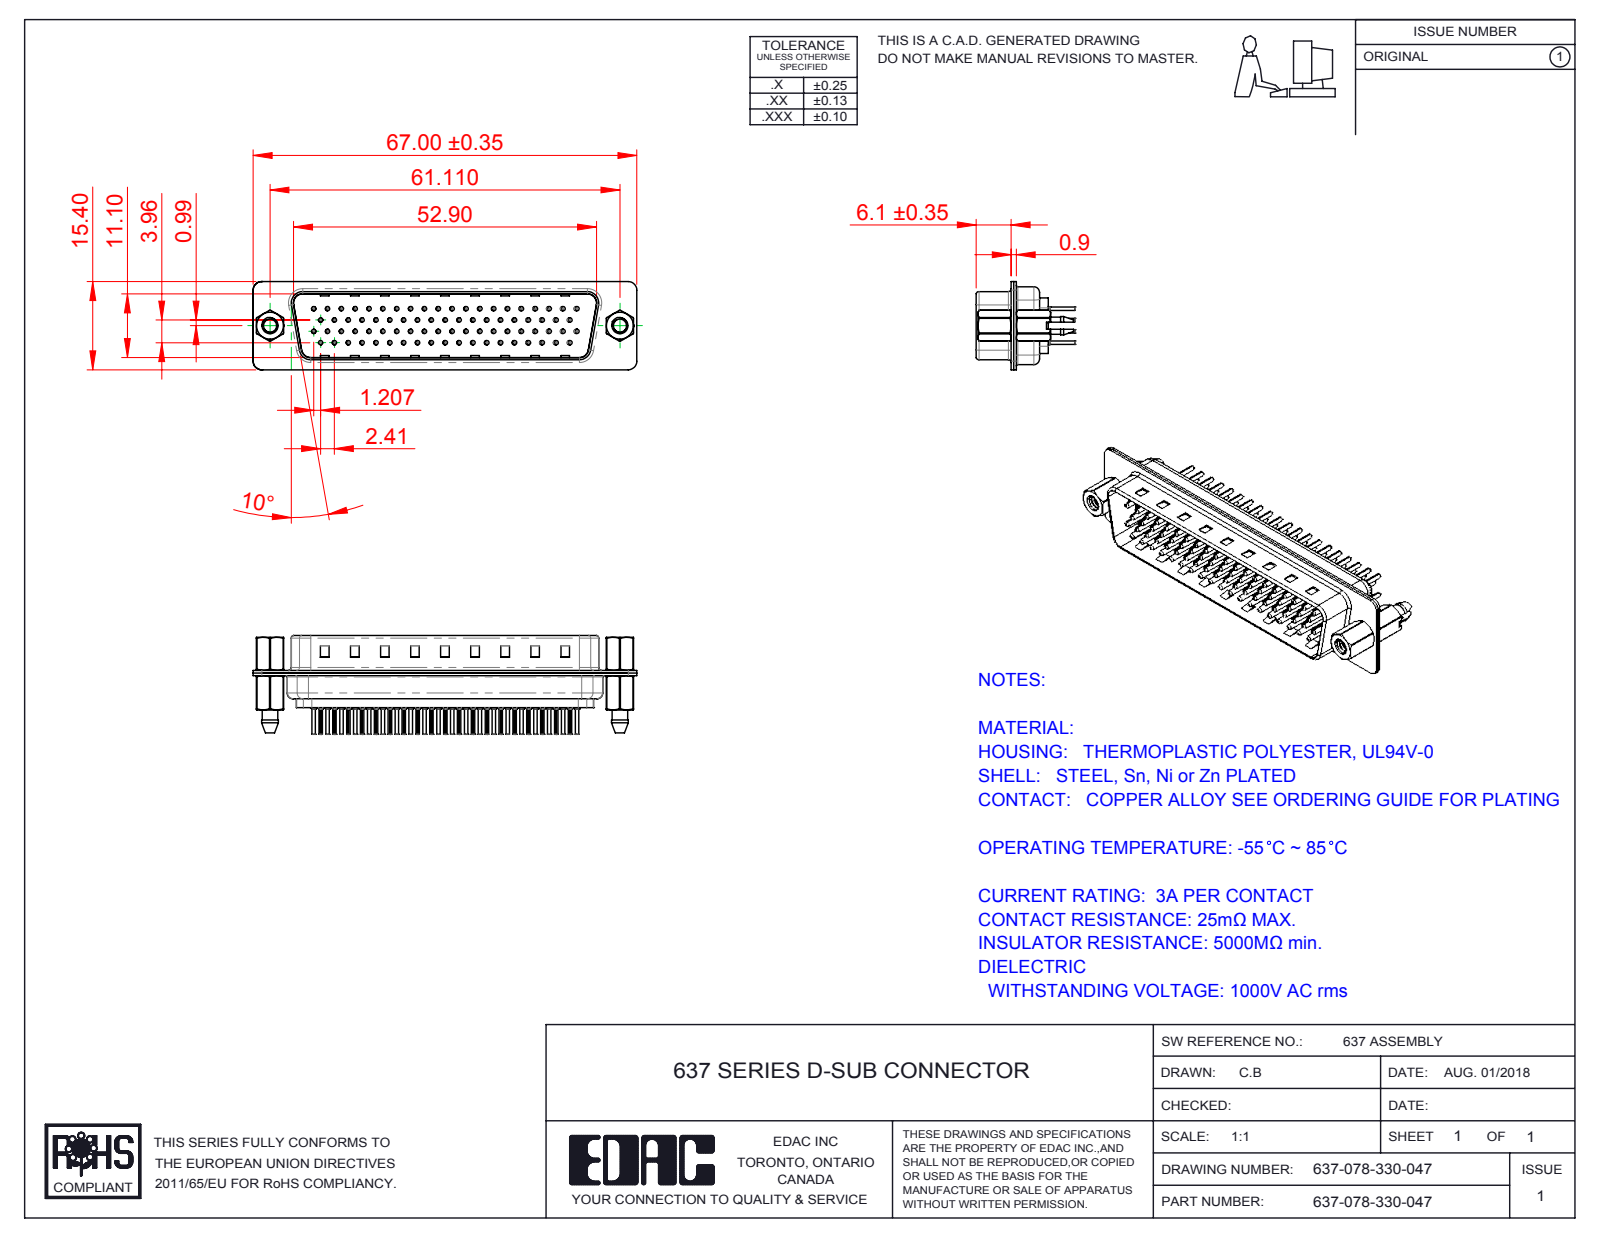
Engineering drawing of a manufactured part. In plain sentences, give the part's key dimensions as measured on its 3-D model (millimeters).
The part is named "637 Contact Row 3_30; 637 Shell Rear_78 Contacts; 637 Contact Row 78_30; 637 Contact Row 1_30 (+6 more)". Its 3-D file was written by "SolidWorks 2016 (CONFIG_CONTROL_DESIGN)". It is 85 solids with 8412 faces: 2129 planar, 3131 cylindrical and 3152 other. Overall it measures 67 by 17.25 by 15.4 millimeters. Its volume is 4 660 cubic millimeters and its surface area 16 633 square millimeters. Round holes: 150 of diameter 1.6, 78 of diameter 0.2, 78 of diameter 0.35, 78 of diameter 1.1, 72 of diameter 0.75, 72 of diameter 2, 3 of diameter 4, 2 of diameter 2.26, 2 of diameter 2.29, 2 of diameter 4.8. Round bosses or shafts: 78 of diameter 2, 78 of diameter 1.5, 78 of diameter 0.75, 78 of diameter 0.6, 2 of diameter 4.9, 2 of diameter 2.79, 1 of diameter 4.8. Partial cylindrical surfaces (rounded edges, fillets, slot ends): 156 of radius 0.1, 18 of radius 1.5, 12 of radius 2, 8 of radius 0.5, 6 of radius 1.6, 4 of radius 0.25, 4 of radius 0.55, 4 of radius 0.7. The main face-to-face distances are 0.45, 0.4, 1.95, 1.5, 11.9, 11.5, 0.7, 11.1, 0.9, 0.8. The hole center spacings are 2.41, 7.24, 6.06, 9.65, 6.96, 8.46, 14.54, 16.89.
